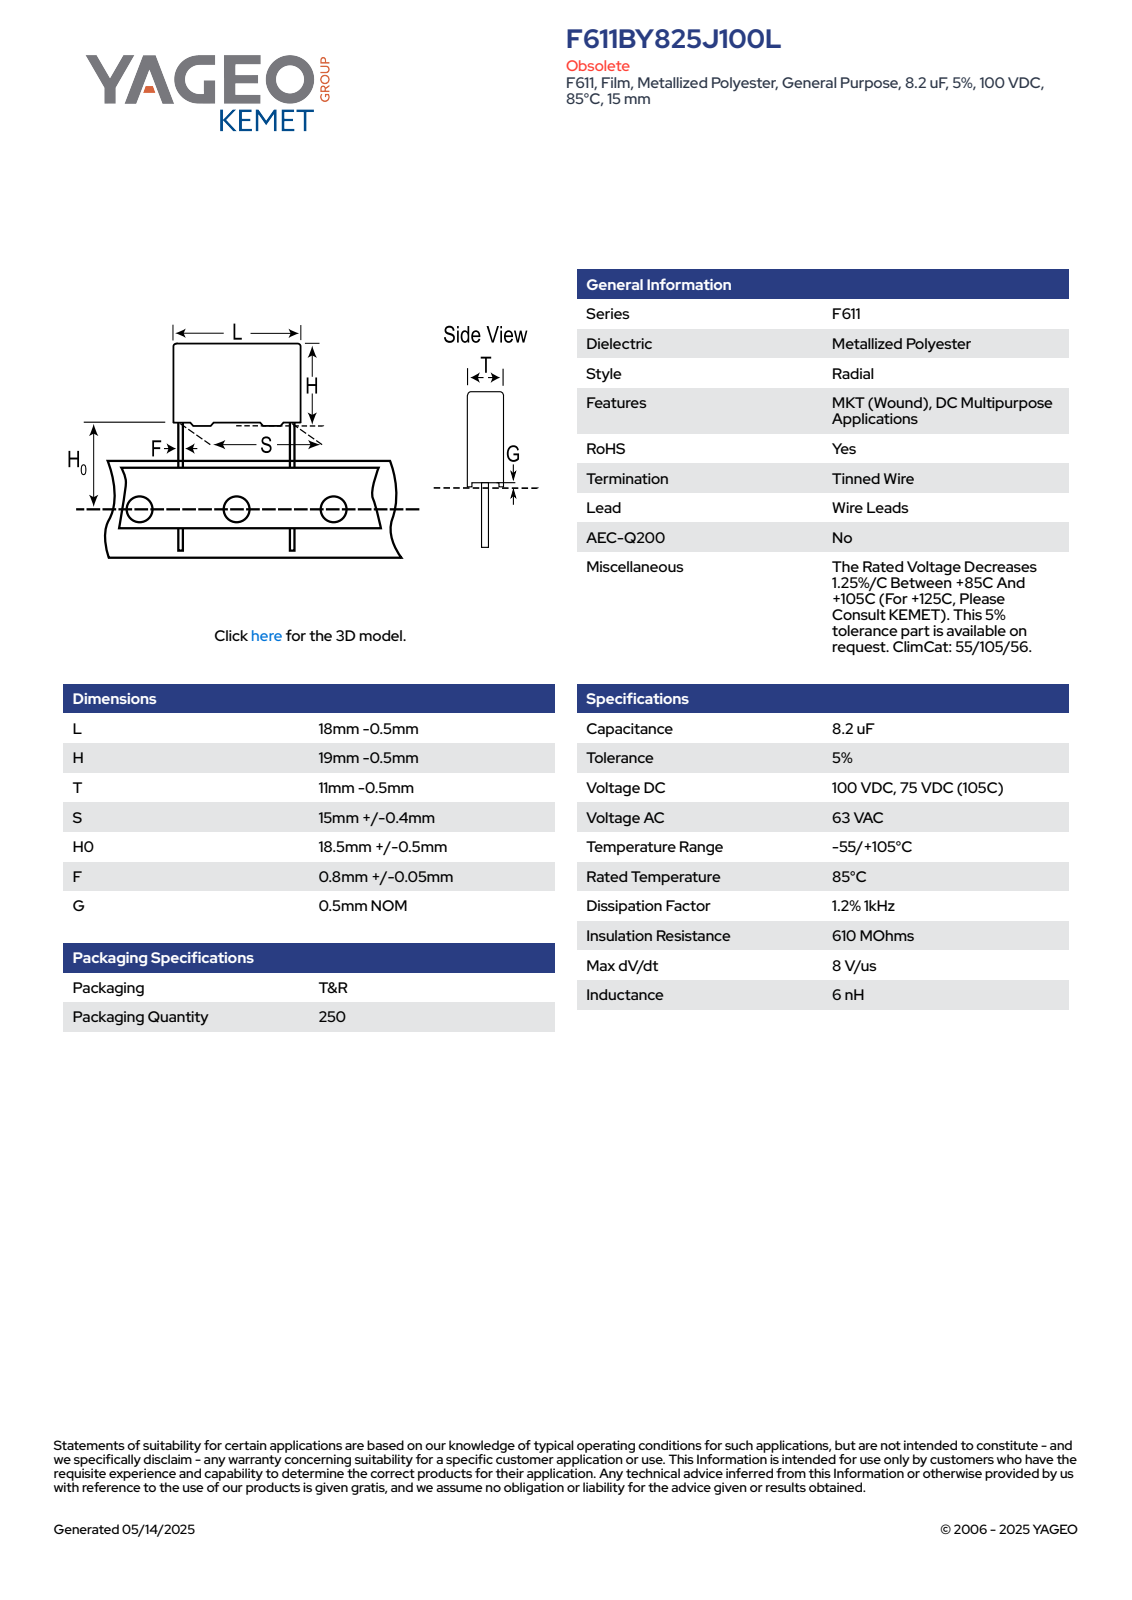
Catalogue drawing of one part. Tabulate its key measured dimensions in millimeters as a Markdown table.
| quantity | value |
| --- | --- |
| part name | CFR_RBG_18X19X11_L17.5H18.5T10.5S15H019F0.85G0.5 |
| STEP written by | SolidWorks 2014 (AUTOMOTIVE_DESIGN) |
| units | millimeters |
| bodies | 4 solids, 89 faces (81 planar, 8 cylindrical, 0 other) |
| overall size | 37.5 × 17.5 × 10.51 |
| volume | 3 330 mm³ |
| surface area | 1 514 mm² |
| round bosses / shafts (diameter × count) | 0.85 × 2 |
| partial cylindrical surfaces (radius × count) | 0.5 × 4 |
| main face-to-face distances | 10.5, 17.5, 18, 10.51, 0.5, 18.5, 0.6, 9.9, 0.61, 9.3 |
